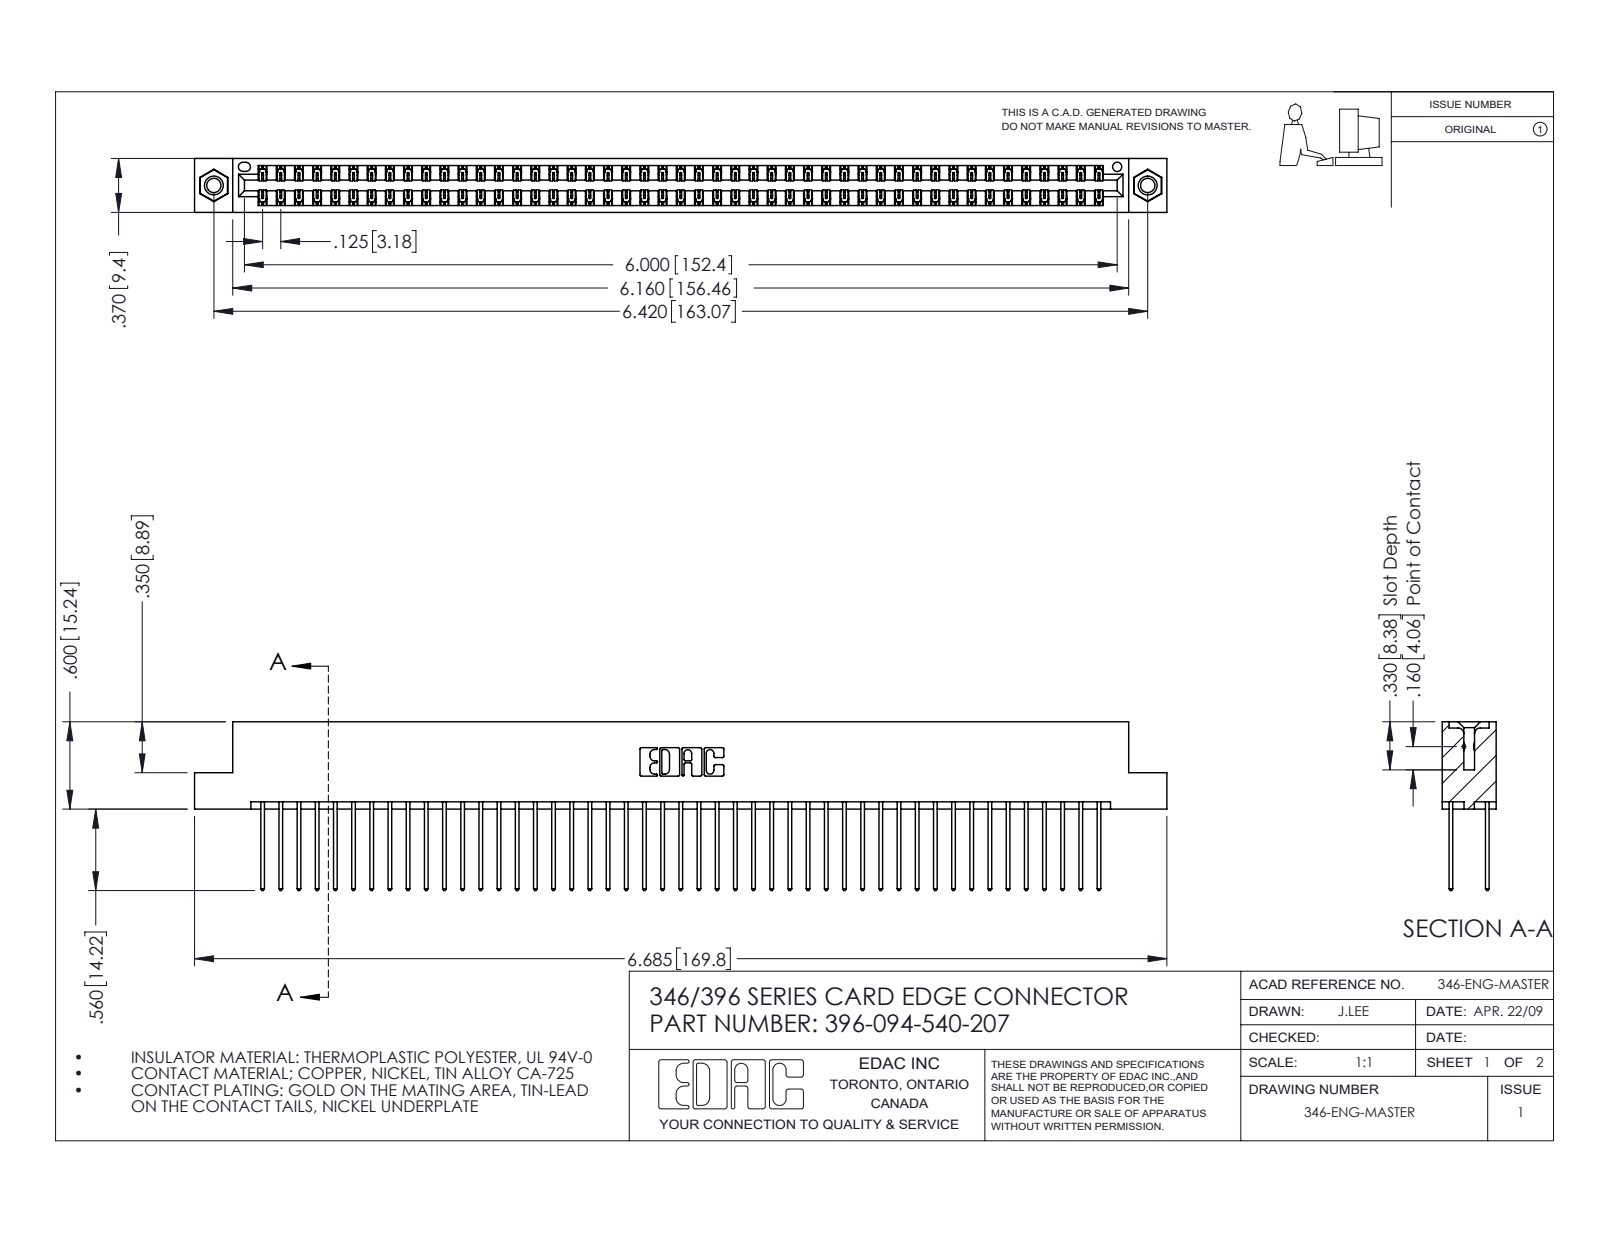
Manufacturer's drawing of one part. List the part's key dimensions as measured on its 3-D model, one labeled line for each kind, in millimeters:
Part name (STEP PRODUCT): 396-094-540-207; 345-292-001_345-293-140; 345-250-001_345-250-005-103; 346 Part_Flush Mounting Lugs - 0.156 Dia-TI
STEP written by: SolidWorks 2016 (CONFIG_CONTROL_DESIGN)
Units: millimetres
Bodies: 97 solids, 5070 faces (3398 planar, 1656 cylindrical, 16 other)
Overall size (bounding box): 169.8 × 29.5 × 9.4
Volume: 16 940 mm³ · Surface area: 25 080 mm²
Round holes (diameter × count): ⌀2.5 ×2, ⌀3.2 ×2, ⌀4 ×2, ⌀1.6 ×1
Round bosses / shafts (diameter × count): ⌀3.9 ×2
Partial cylindrical surfaces — rounded edges, fillets, slot ends (radius × count): R0.2 ×141, R0.3 ×94, R0.3 ×22, R0.2 ×6, R0.8 ×6, R0.7 ×3, R0.4 ×2, R0.6 ×2
Main face-to-face distances: 1.2, 8.2, 6.4, 1.8, 7.6, 0.6, 9.4, 7, 3.8, 5.6
Hole centre spacings: 6.2, 157.8, 163.1
